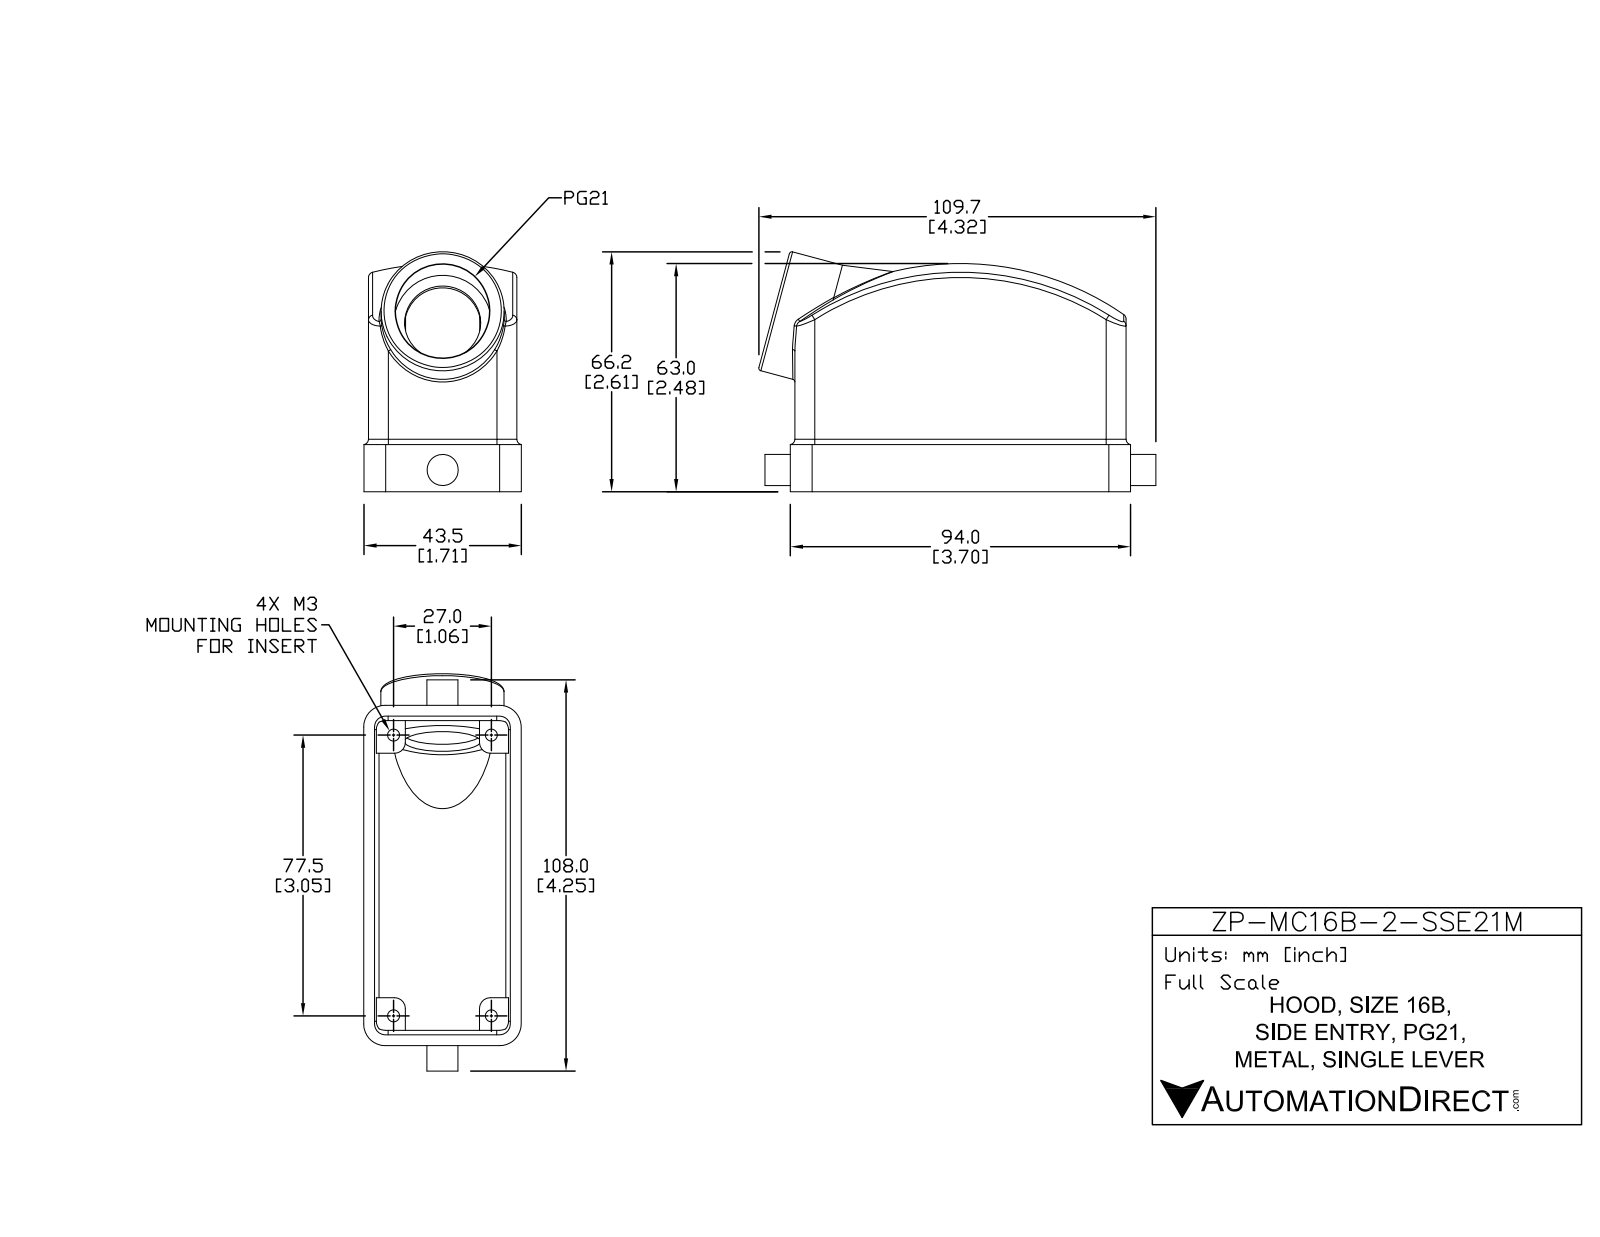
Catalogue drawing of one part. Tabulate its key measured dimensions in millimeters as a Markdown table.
| quantity | value |
| --- | --- |
| part name | ZP-MC16B-2-SSE21M |
| STEP written by | SolidWorks 2017 (AUTOMOTIVE_DESIGN) |
| units | millimeters |
| bodies | 3 solids, 130 faces (48 planar, 50 cylindrical, 32 other) |
| overall size | 109.72 × 66.26 × 43.5 |
| volume | 61 154 mm³ |
| surface area | 38 277 mm² |
| round holes (diameter × count) | 3.5 × 4, 21 × 1, 27 × 1 |
| round bosses / shafts (diameter × count) | 34 × 1, 8.6 × 1 |
| partial cylindrical surfaces (radius × count) | 3 × 8, 1.5 × 4, 4 × 4, 4.5 × 4, 5.5 × 4, 6 × 4, 17 × 1 |
| main face-to-face distances | 3, 1.25, 38, 39.25, 41, 4.25, 35, 1.75, 42.25, 40.5 |
| hole center spacings | 27, 77.5, 82.07 |
